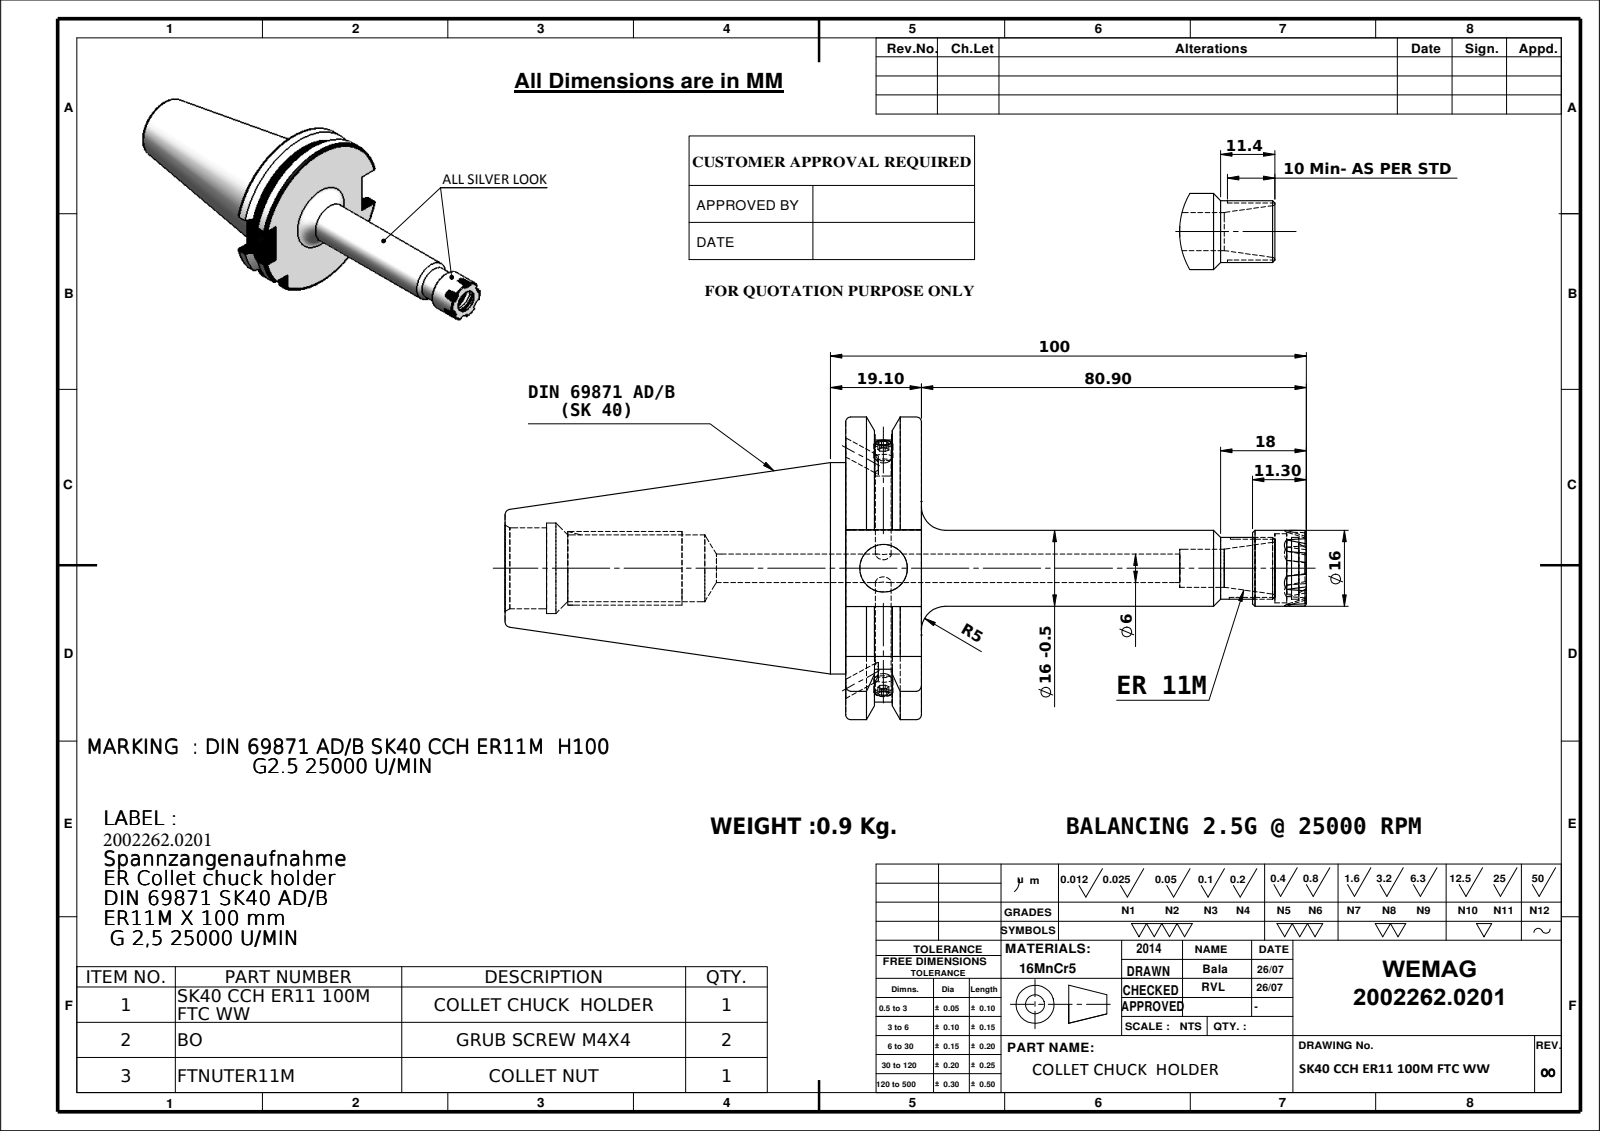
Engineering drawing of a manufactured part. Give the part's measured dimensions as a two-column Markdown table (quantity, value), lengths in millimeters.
| quantity | value |
| --- | --- |
| part name | SK40 CCH ER11 100M FTC WW; M4X4_DIN 913 - M4 x 4-N; FTNUTER11M-11MSPL |
| STEP written by | SolidWorks 2009 (CONFIG_CONTROL_DESIGN) |
| units | millimeters |
| bodies | 4 solids, 185 faces (70 planar, 48 cylindrical, 67 other) |
| overall size | 168.4 × 63.55 × 61.48 |
| volume | 116 171 mm³ |
| surface area | 26 914 mm² |
| round holes (diameter × count) | 3.3 × 1, 6 × 1, 8 × 1, 10 × 1, 11.5 × 1, 12.25 × 1, 13 × 1, 14 × 1, 14.5 × 1, 17 × 1, 19 × 1 |
| round bosses / shafts (diameter × count) | 4 × 2, 44.45 × 1, 16 × 1 |
| partial cylindrical surfaces (radius × count) | 28.12 × 1, 31.77 × 1 |
| main face-to-face distances | 15.9, 16.1, 47.8, 87.5, 71.6, 3.5, 9.87, 6.03, 77.63, 6.12 |
| hole center spacings | 0.75 |
